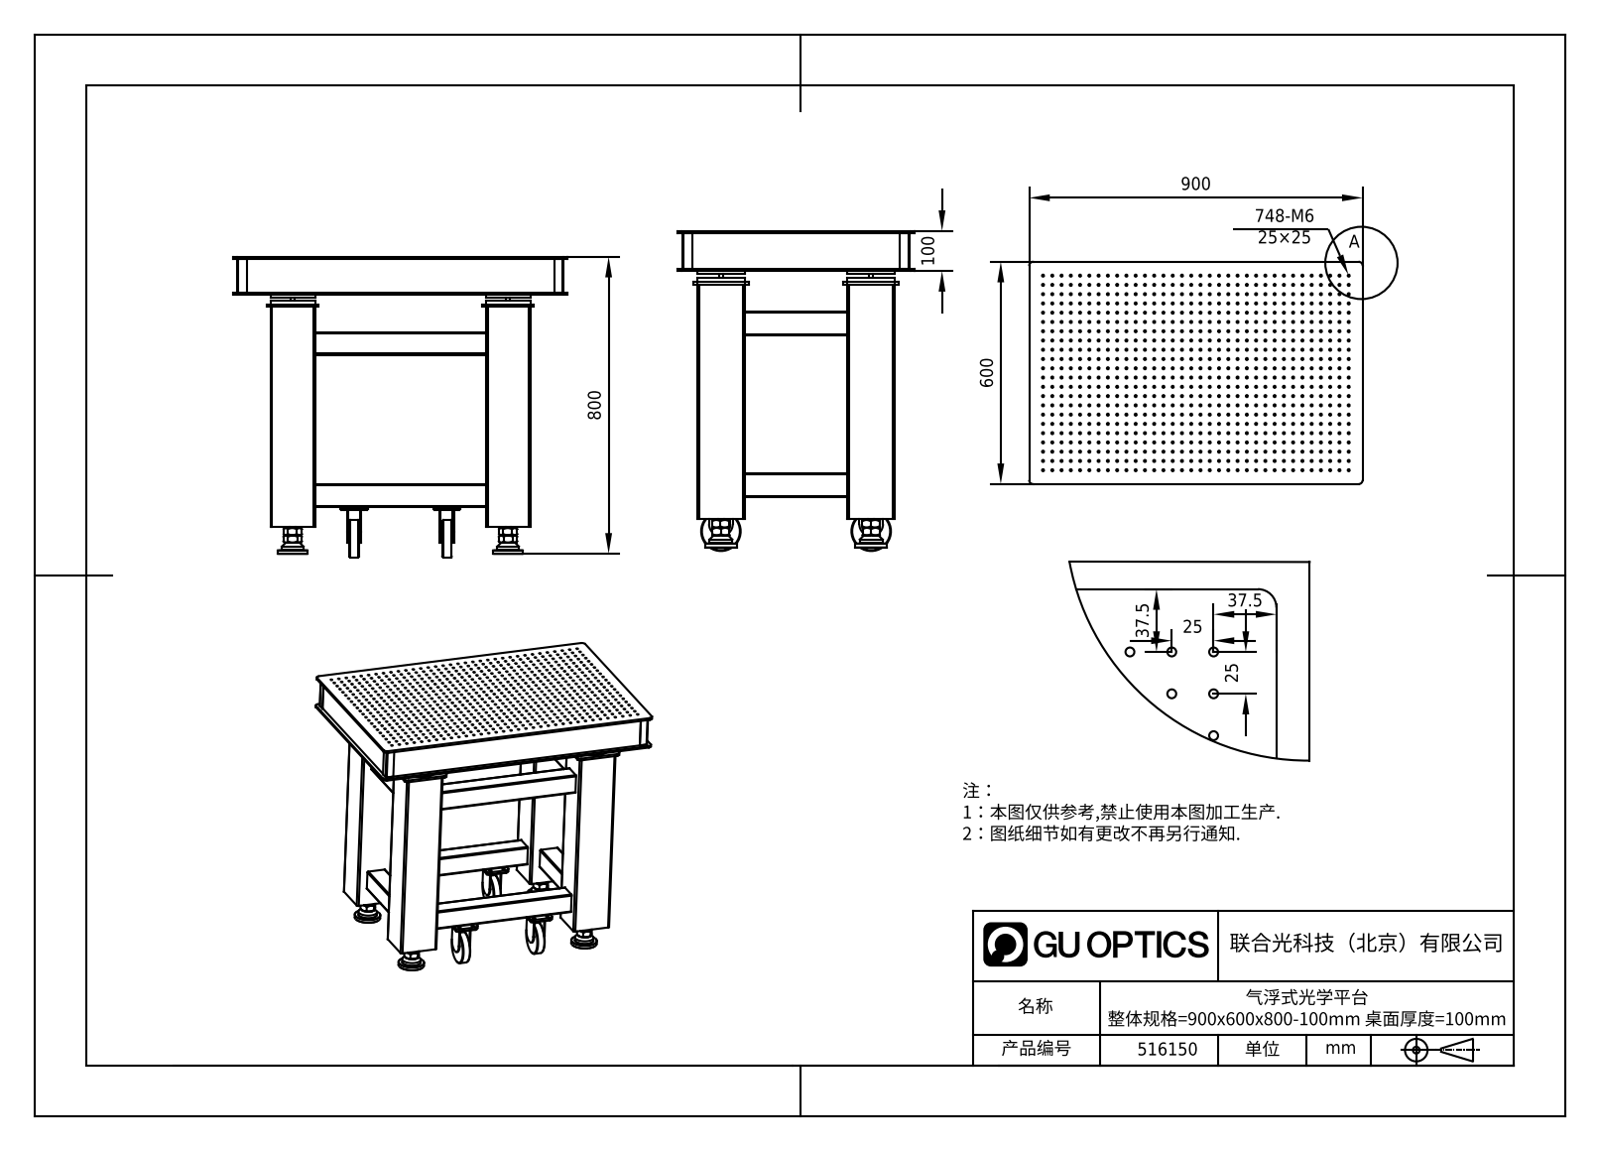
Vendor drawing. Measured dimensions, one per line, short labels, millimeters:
name: 516150
written by: SolidWorks 2020 (CONFIG_CONTROL_DESIGN)
unit: mm
bodies: 62 solids, 3285 faces (1237 planar, 1856 cylindrical, 192 other)
size: 900 × 809 × 600
volume: 59 970 000 mm³; area: 7 017 000 mm²
holes: 748× ⌀5.3, 16× ⌀8.5, 16× ⌀9, 4× ⌀17.5, 4× ⌀22, 4× ⌀28, 4× ⌀43
bosses: 4× ⌀120, 4× ⌀80, 4× ⌀58, 4× ⌀14, 4× ⌀10, 2× ⌀100
rounds: 48× R1, 48× R10, 36× R3, 16× R5, 16× R7, 4× R2, 4× R11, 2× R30
face distances: 4, 116, 580, 5, 2, 58, 380, 96, 101, 120
hole spacings: 380, 25, 45, 50, 78, 90.05, 147.74, 191.51
